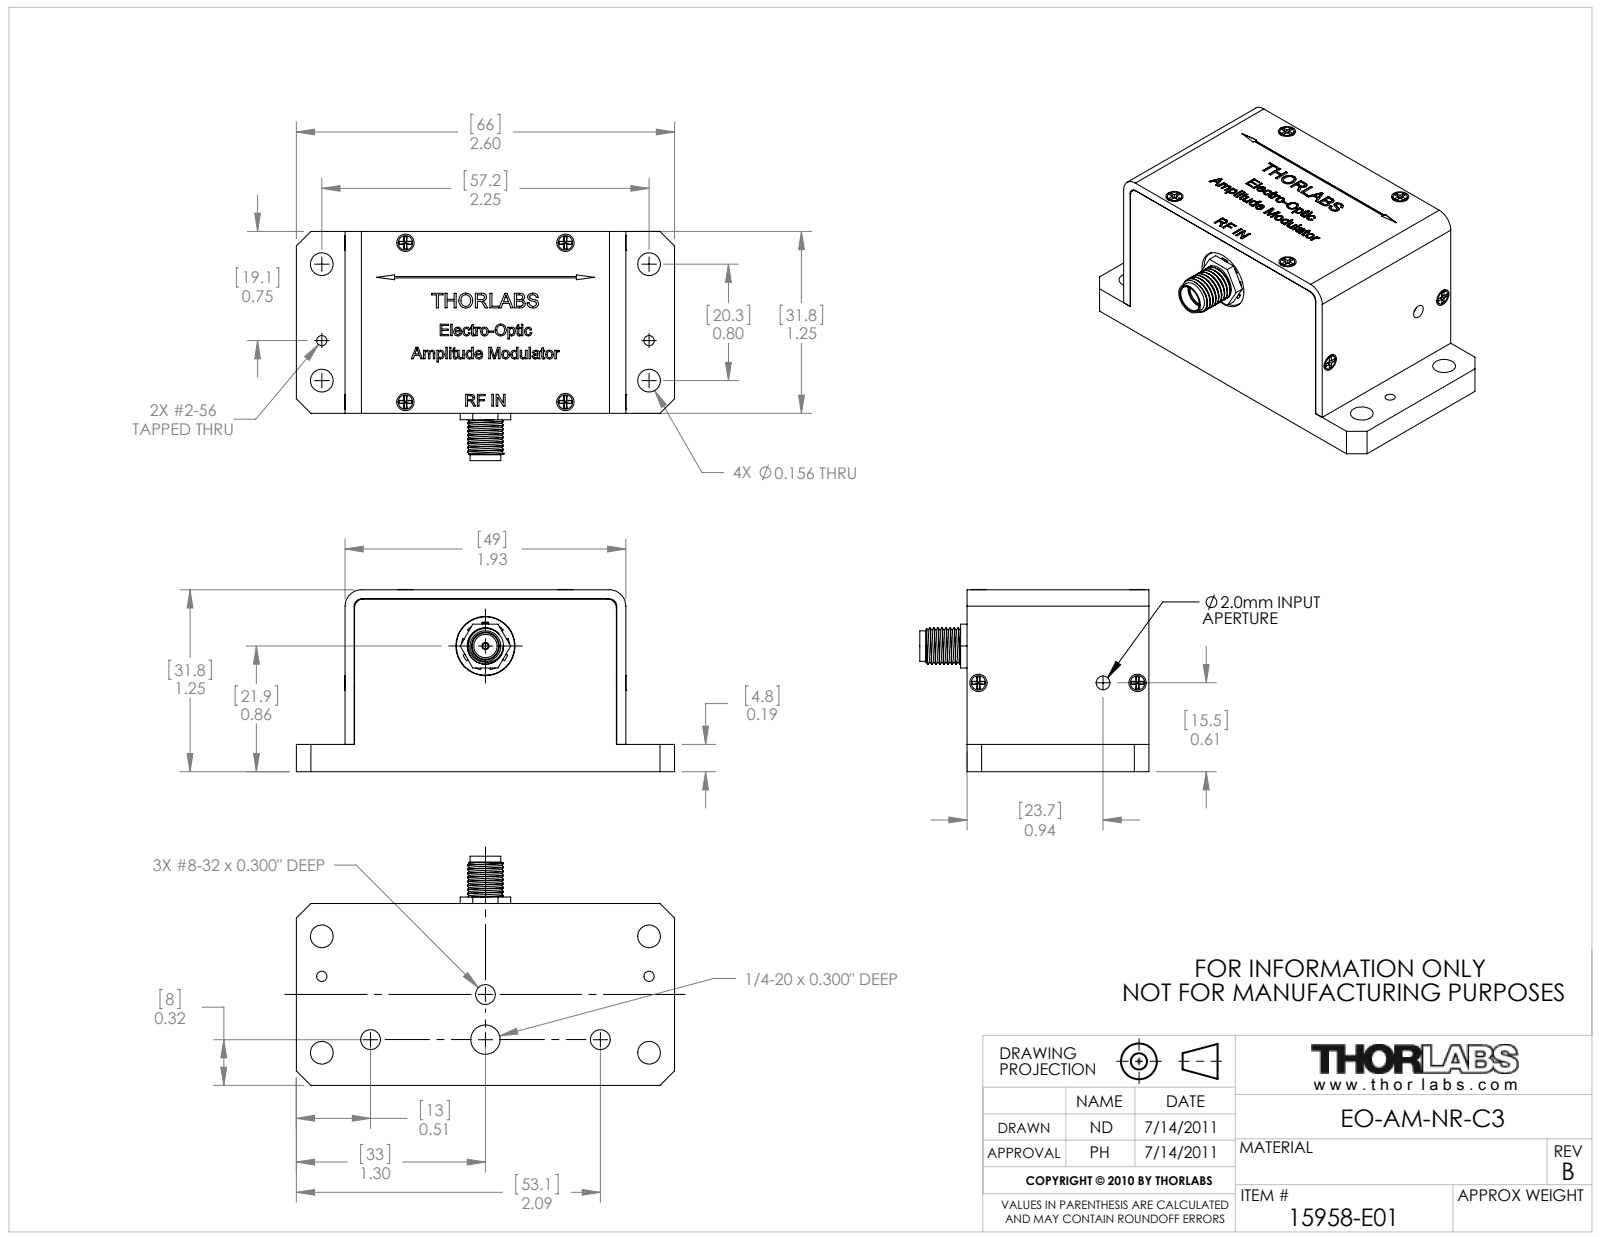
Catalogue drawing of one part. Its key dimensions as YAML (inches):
part_name: "15958-E01"
step_written_by: "SolidWorks 2011 (AUTOMOTIVE_DESIGN)"
units: inches
bodies: {solids: 13, faces: 1048, planar: 588, cylindrical: 172, other: 288}
overall_size: [2.6, 1.575, 1.252]
volume: 1.722
surface_area: 29.17
round_holes:
  - {diameter: 0.07, count: 8}
  - {diameter: 0.047, count: 6}
  - {diameter: 0.156, count: 4}
  - {diameter: 0.136, count: 3}
  - {diameter: 0.037, count: 1}
  - {diameter: 0.05, count: 1}
  - {diameter: 0.094, count: 1}
  - {diameter: 0.16, count: 1}
  - {diameter: 0.165, count: 1}
  - {diameter: 0.181, count: 1}
  - {diameter: 0.201, count: 1}
  - {diameter: 0.25, count: 1}
round_bosses_or_shafts:
  - {diameter: 0.099, count: 6}
  - {diameter: 0.06, count: 6}
  - {diameter: 0.4, count: 1}
  - {diameter: 0.315, count: 1}
  - {diameter: 0.248, count: 1}
  - {diameter: 0.21, count: 1}
  - {diameter: 0.05, count: 1}
partial_cylinders:
  - {radius: 0.063, count: 5}
  - {radius: 0.05, count: 2}
  - {radius: 0.113, count: 2}
  - {radius: 0.128, count: 2}
  - {radius: 0.137, count: 1}
  - {radius: 0.165, count: 1}
face_to_face_distances: [1.25, 0.125, 1.125, 1.188, 0.063, 1.867, 1, 0.062, 0.35, 0.838]
hole_center_spacings: [0.594, 0.776, 1.108, 1.194, 1.681, 1.924, 1.094, 2.25]
